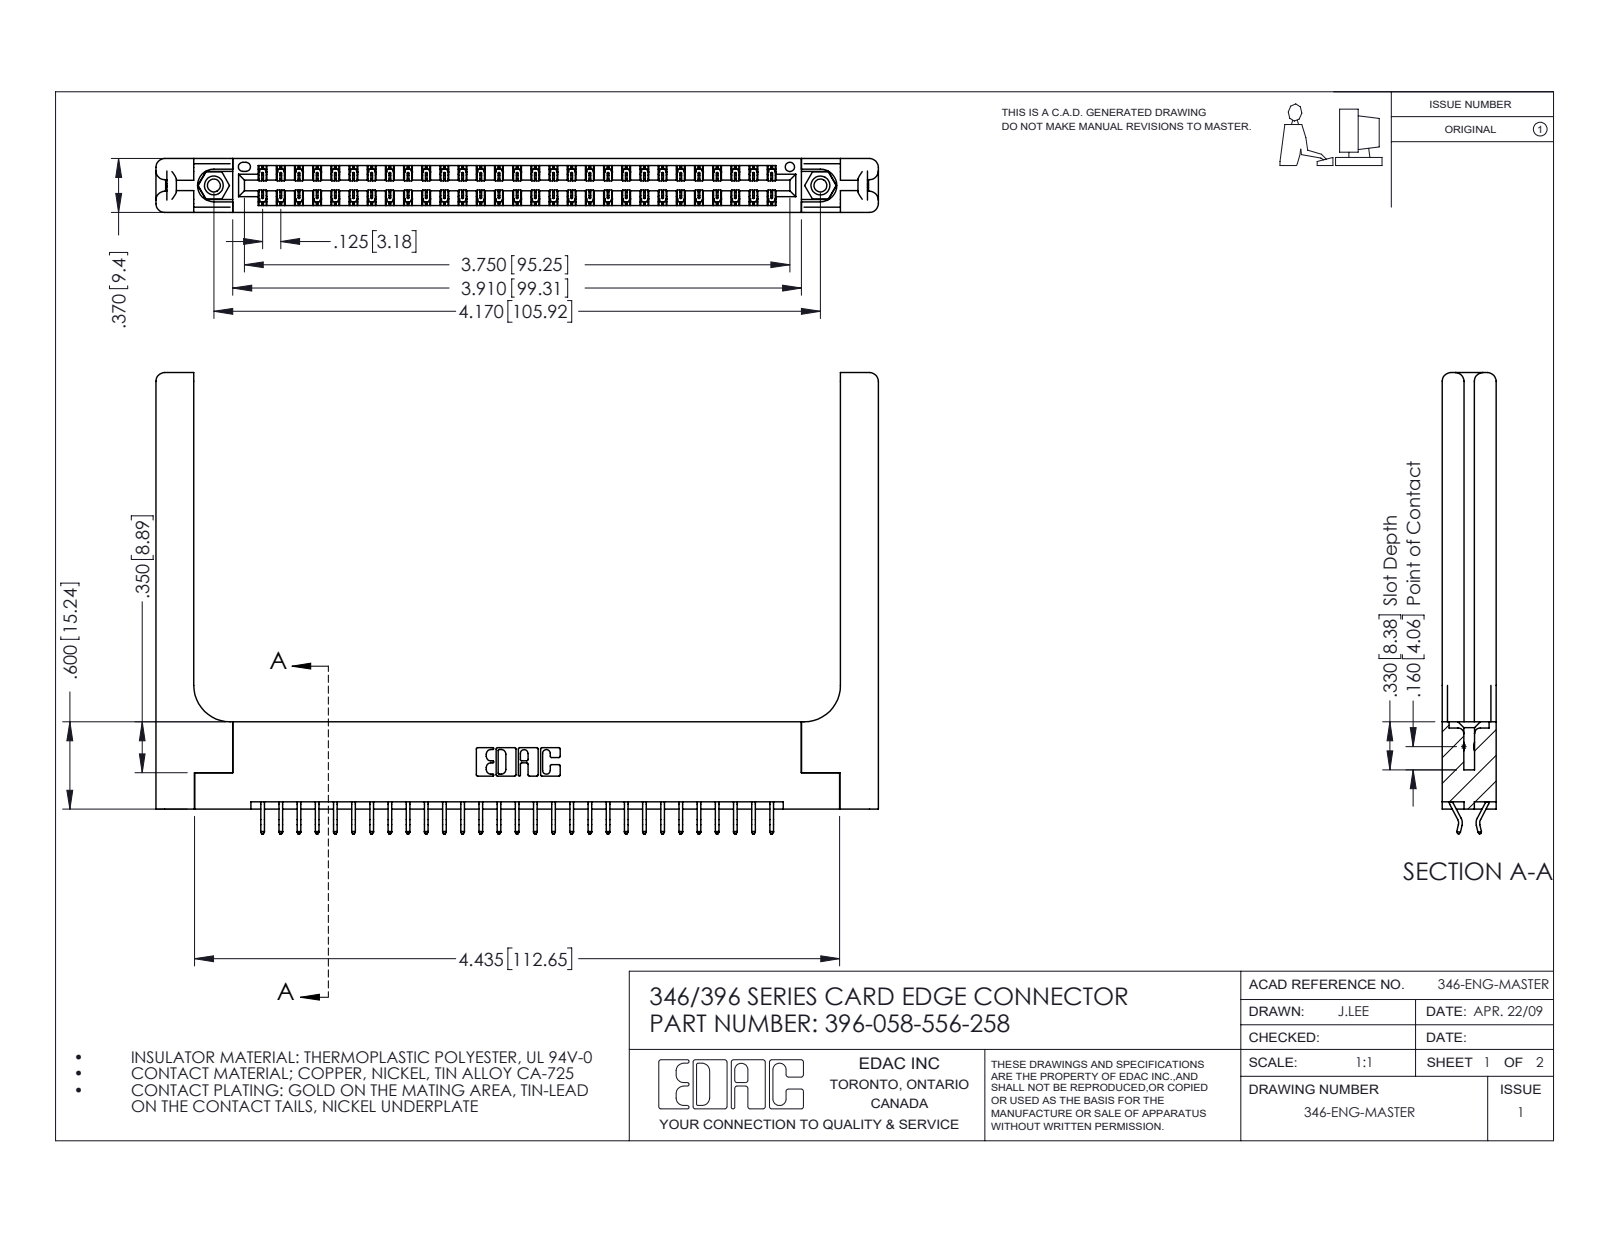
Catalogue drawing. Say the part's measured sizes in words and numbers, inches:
The part is named "345-292-001_556 Tail; 396-058-556-258; 346-220-058_345-220-058; 345-250-001_345-250-001-102 (+1 more)". Its 3-D file was written by "SolidWorks 2016 (CONFIG_CONTROL_DESIGN)". It is 63 solids with 3742 faces: 2486 planar, 1196 cylindrical and 60 other. Overall it measures 4.966 by 3.17 by 0.37 inches. Its volume is 1.202 cubic inches and its surface area 33.29 square inches. Round holes: 2 of diameter 0.089, 2 of diameter 0.125, 2 of diameter 0.156, 1 of diameter 0.064. Round bosses or shafts: 2 of diameter 0.155. Partial cylindrical surfaces (rounded edges, fillets, slot ends): 87 of radius 0.006, 22 of radius 0.01, 16 of radius 0.06, 6 of radius 0.007, 6 of radius 0.031, 3 of radius 0.026, 2 of radius 0.01, 2 of radius 0.014. The main face-to-face distances are 0.37, 0.048, 0.322, 0.072, 0.15, 0.148, 0.25, 0.025, 0.298, 0.275. The hole center spacings are 0.246, 3.962, 4.17.
